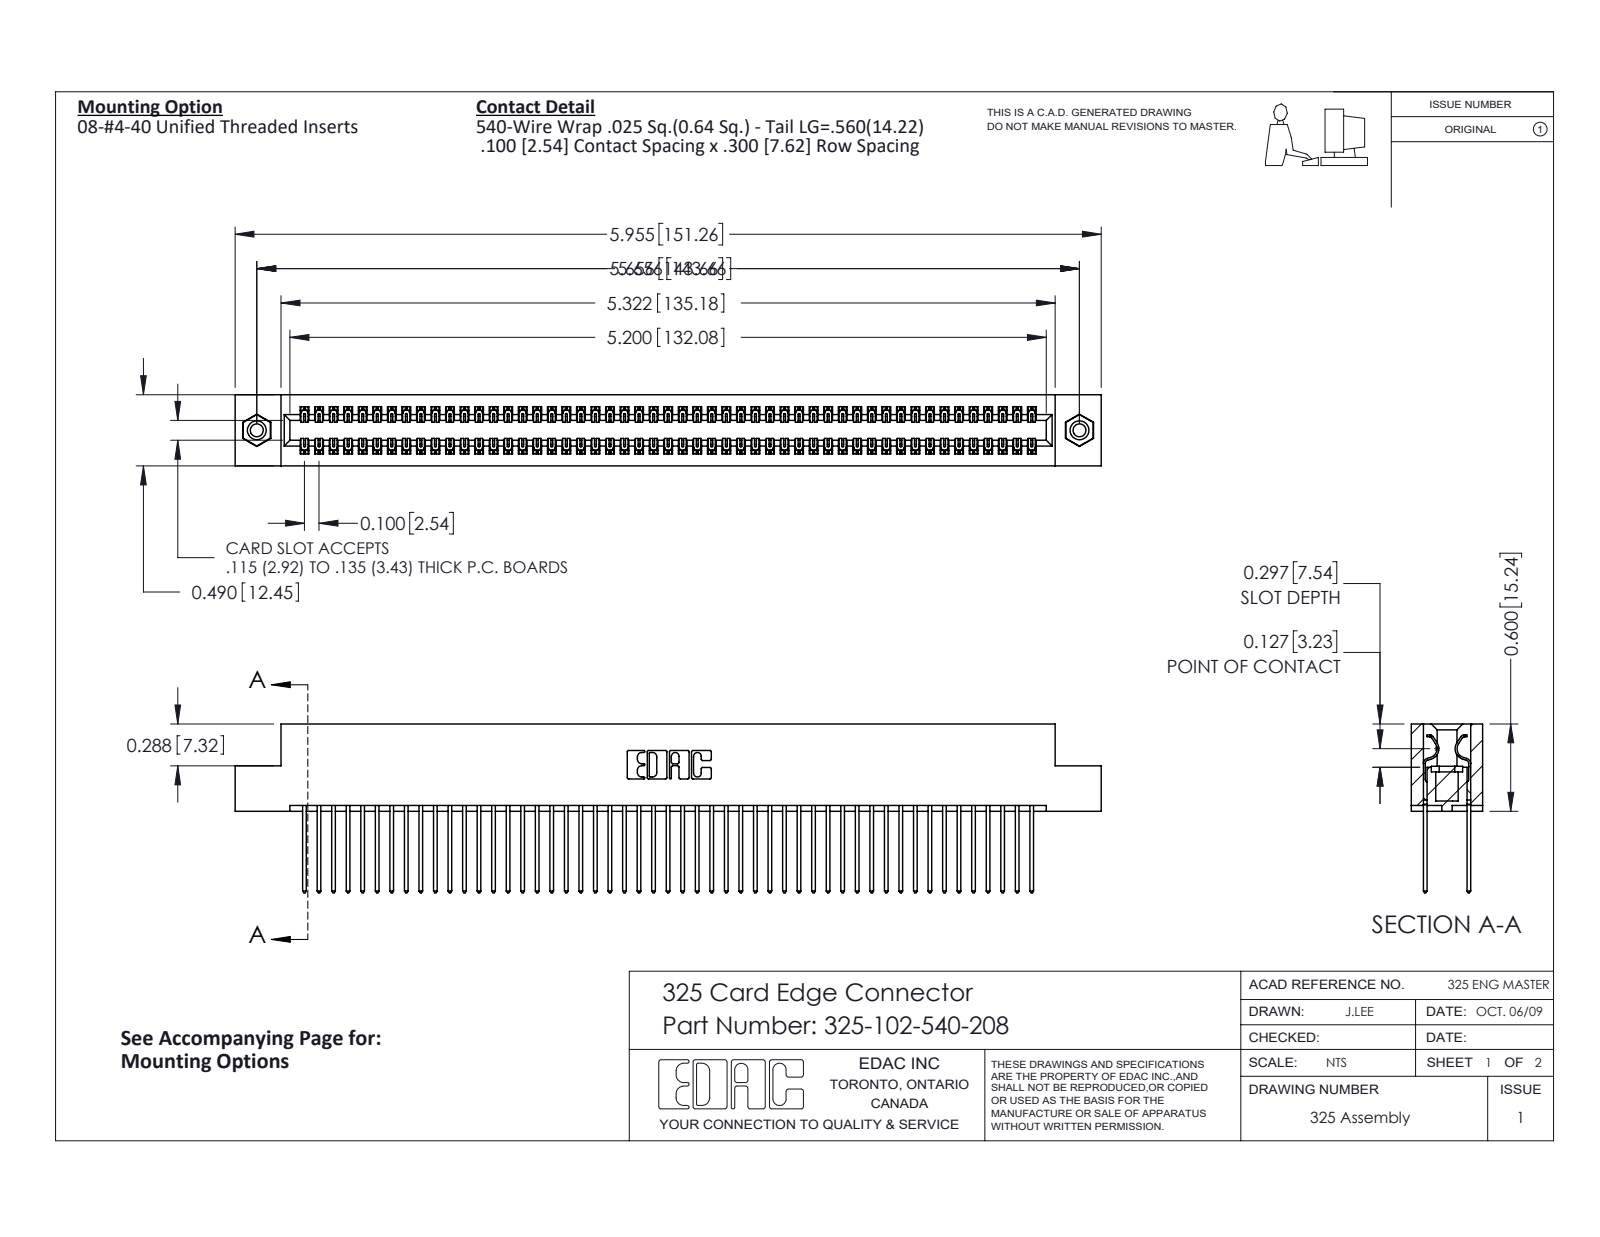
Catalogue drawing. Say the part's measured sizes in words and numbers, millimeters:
The part is named "325 Part_TI; 325-292-001_325-293-140; 345-250-001_345-250-003-102; 325-102-540-208". Its 3-D file was written by "SolidWorks 2016 (CONFIG_CONTROL_DESIGN)". It is 105 solids with 5478 faces: 3774 planar, 1688 cylindrical and 16 other. Overall it measures 151.3 by 29.5 by 12.4 millimeters. Its volume is 19 990 cubic millimeters and its surface area 26 260 square millimeters. Round holes: 2 of diameter 2.3, 2 of diameter 3.2, 2 of diameter 4.1. Round bosses or shafts: 2 of diameter 3.9. Partial cylindrical surfaces (rounded edges, fillets, slot ends): 153 of radius 0.2, 102 of radius 0.3, 22 of radius 0.3, 6 of radius 0.2, 6 of radius 0.8, 3 of radius 0.7, 2 of radius 0.4, 2 of radius 0.6. The main face-to-face distances are 2.1, 10.3, 7.6, 2.7, 9.7, 0.6, 8.3, 12.4, 7, 14.2. The hole center spacings are 143.7.
